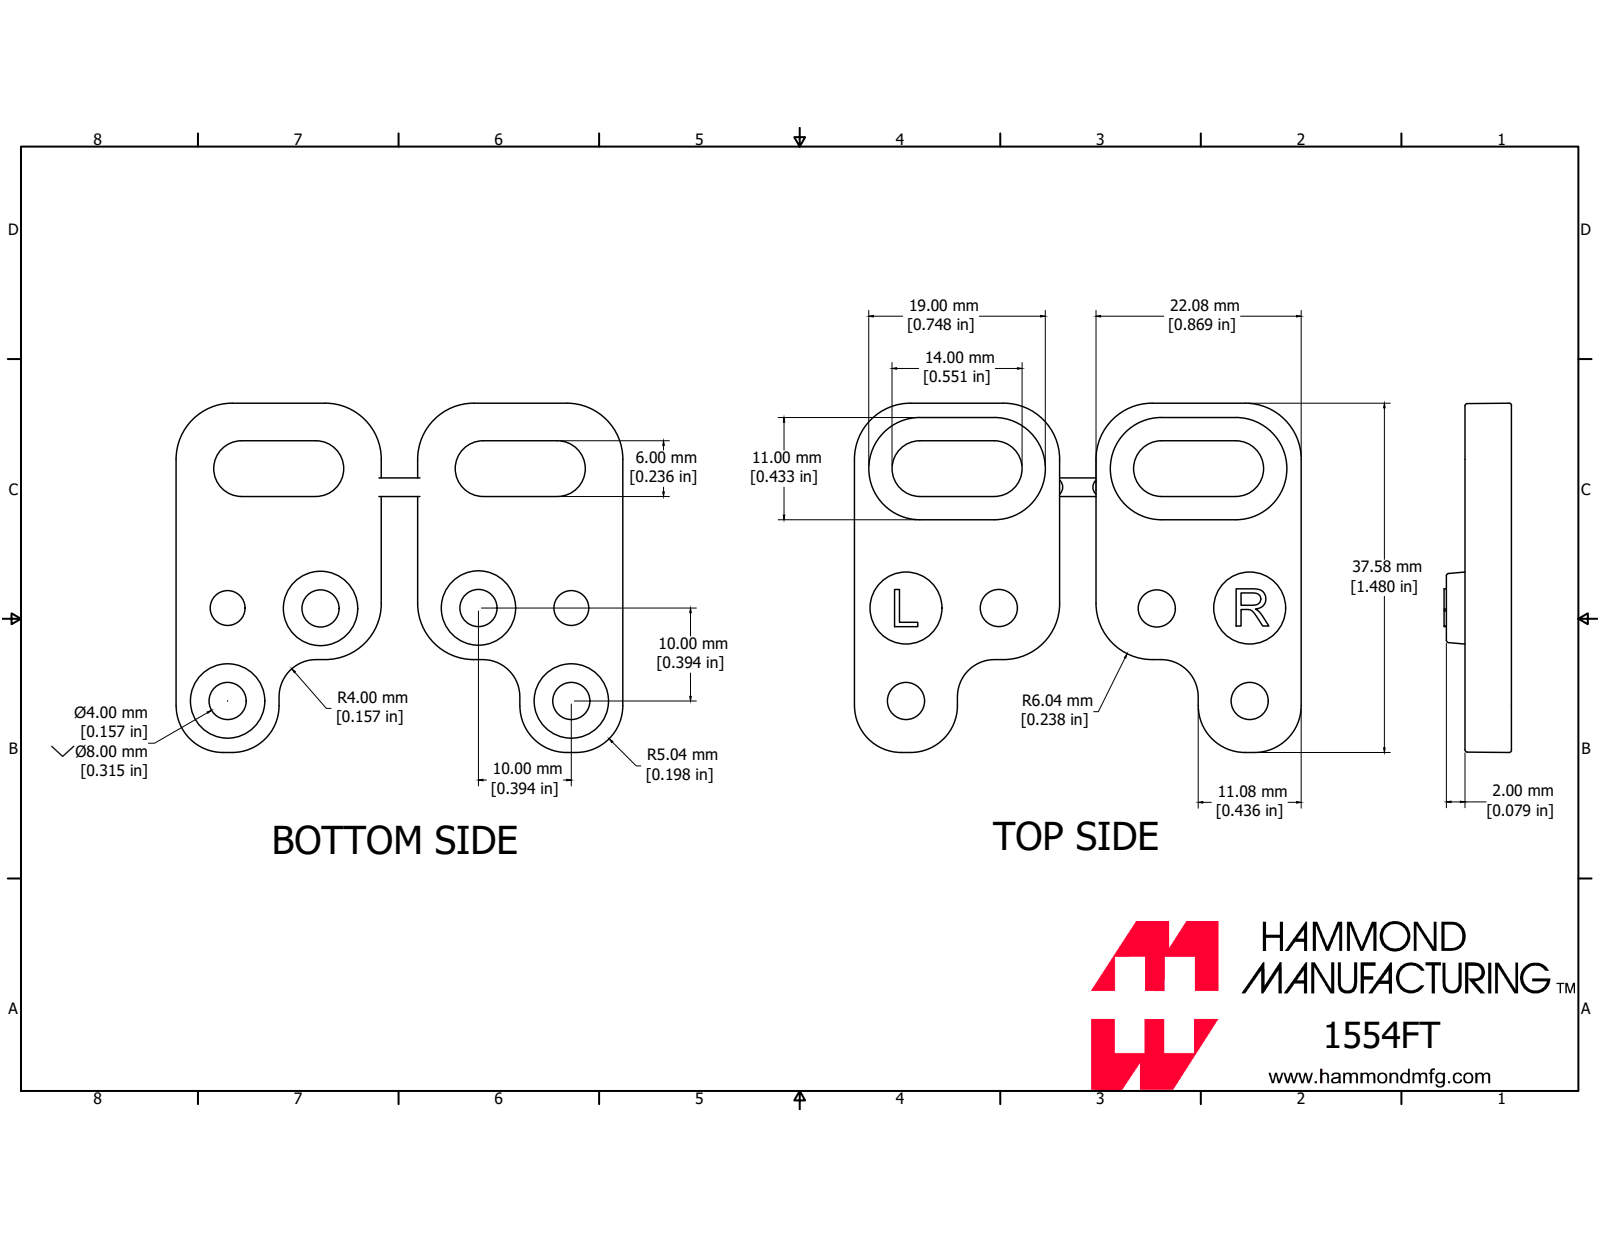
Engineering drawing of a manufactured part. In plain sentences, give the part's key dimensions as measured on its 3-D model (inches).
The part is named "1554FT". Its 3-D file was written by "SolidWorks 2019 (CONFIG_CONTROL_DESIGN)". It is 4 solids with 280 faces: 96 planar, 68 cylindrical and 116 other. Overall it measures 2.155 by 1.924 by 0.925 inches. Its volume is 0.676 cubic inches and its surface area 12.53 square inches. Round holes: 8 of diameter 0.157. Partial cylindrical surfaces (rounded edges, fillets, slot ends): 48 of radius 0.01, 8 of radius 0.118, 4 of radius 0.157. The main face-to-face distances are 0.197, 0.63, 0.305, 0.324, 0.306, 0.628, 0.127, 0.431, 0.433, 0.826. The hole center spacings are 0.557, 0.325, 0.666, 0.238, 0.399, 0.469, 0.548, 0.653.
